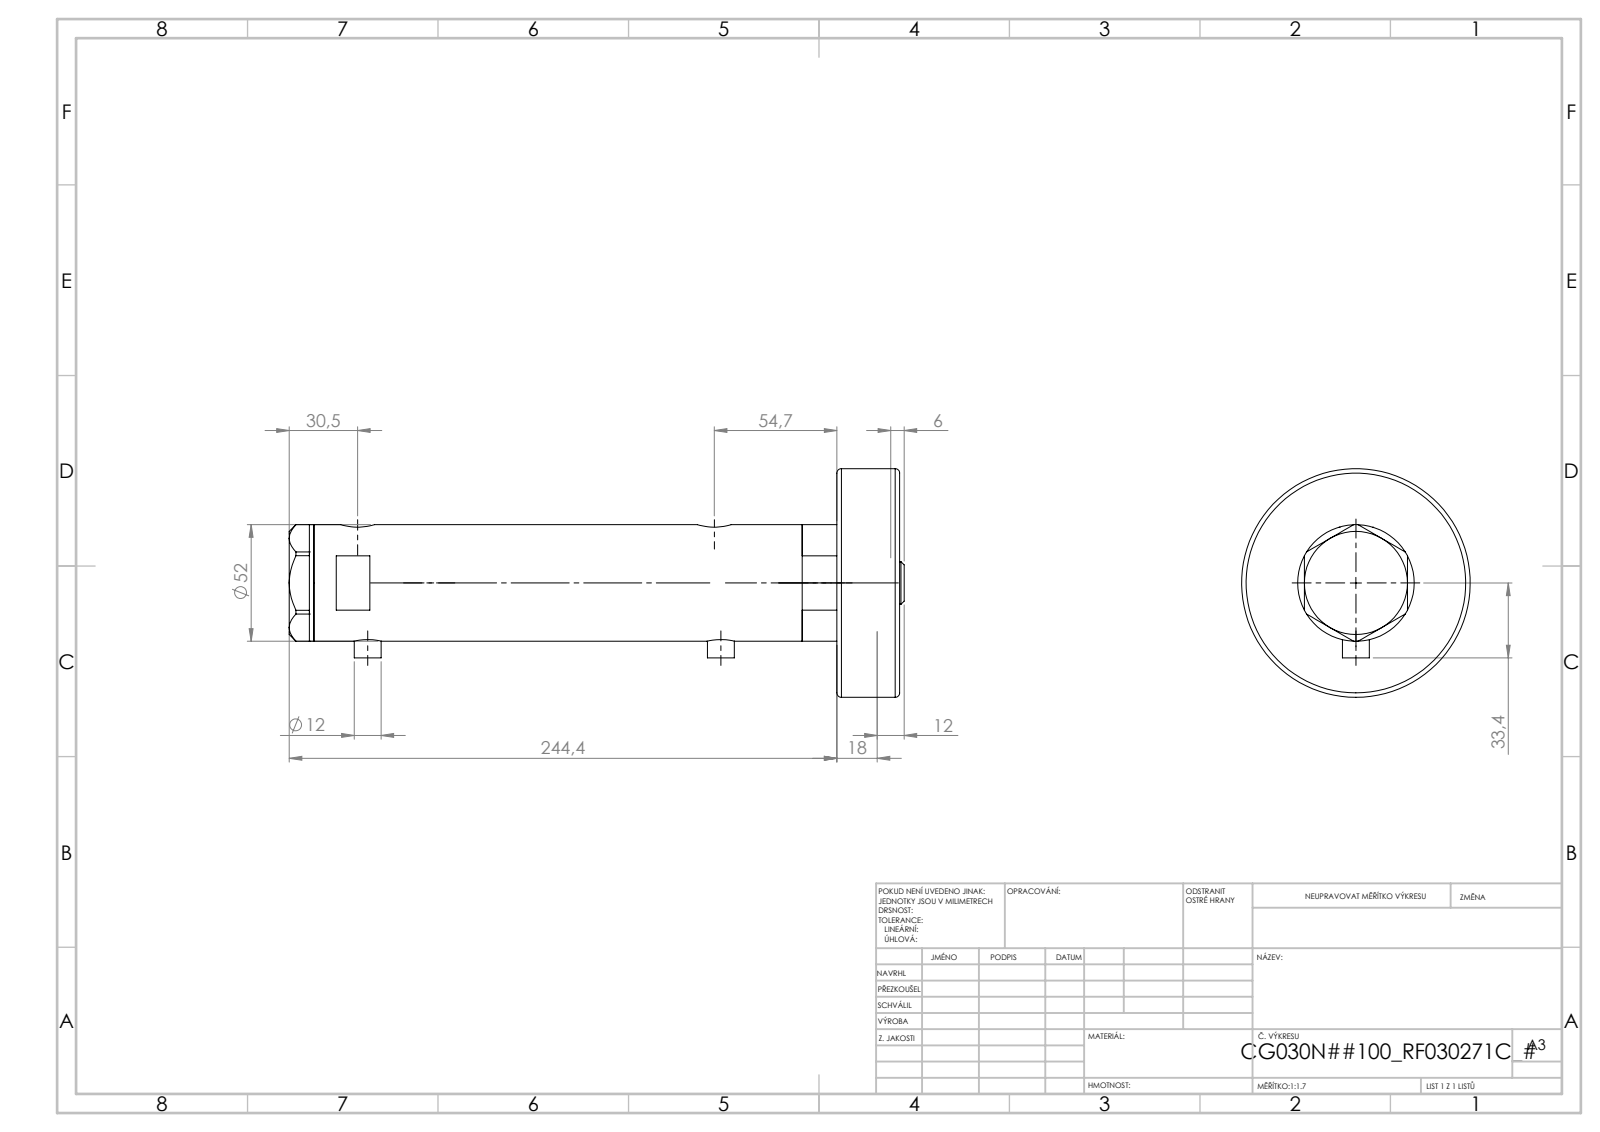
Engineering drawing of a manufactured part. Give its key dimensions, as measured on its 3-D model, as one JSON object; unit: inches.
{"part_name": "V270CG_BACK; V270CG_FRONT; V270CG_VC; V270CG_MIDDLE", "step_written_by": "SolidWorks 2019 (CONFIG_CONTROL_DESIGN)", "units": "inches", "bodies": {"solids": 4, "faces": 140, "planar": 67, "cylindrical": 53, "other": 20}, "overall_size": [9.804, 2.091, 2.047], "volume_in3": 26.89, "surface_area_in2": 150.6, "round_holes": [[0.197, 2], [0.383, 2], [0.492, 2], [0.591, 2], [0.256, 1], [0.787, 1], [0.846, 1], [1.181, 1], [1.299, 1], [1.732, 1]], "round_bosses_or_shafts": [[0.472, 2], [2.047, 1], [1.575, 1], [1.496, 1], [0.748, 1]], "face_to_face_distances": [6.045, 0.937, 5.108, 0.433, 1.37, 6.478, 1.811, 7.911, 7.478, 6.541], "hole_center_spacings": [0.114, 0.177, 4.99, 5.104, 5.167, 5.281, 0.114, 0.115]}
